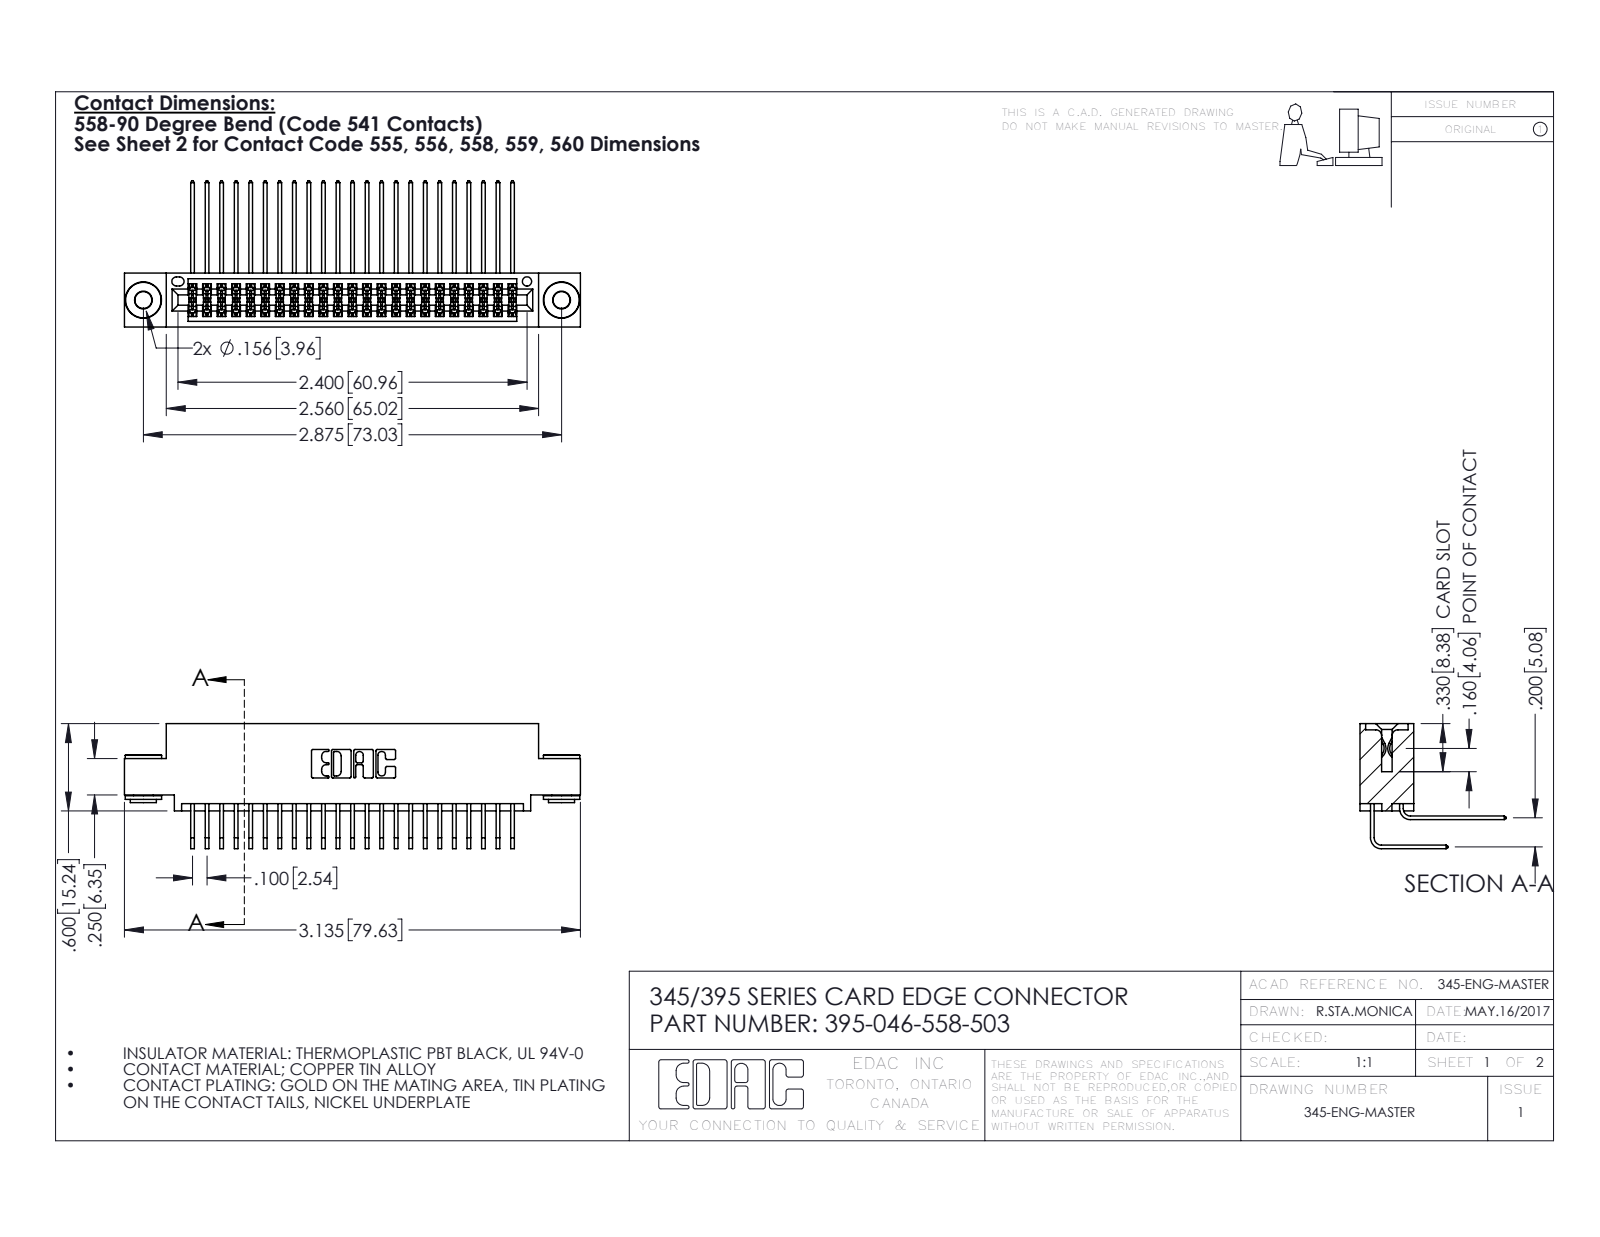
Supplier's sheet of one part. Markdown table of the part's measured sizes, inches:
| quantity | value |
| --- | --- |
| part name | 345-292-001_558 Tail - 2; 345 Part_0.110 Offset - 0.156 Dia-TH; 395-046-558-503; 345-292-001_558 559 Tail - 1 (+1 more) |
| STEP written by | SolidWorks 2016 (CONFIG_CONTROL_DESIGN) |
| units | inches |
| bodies | 49 solids, 2560 faces (1704 planar, 848 cylindrical, 8 other) |
| overall size | 3.135 × 1.005 × 0.859 |
| volume | 0.474 in³ |
| surface area | 19.63 in² |
| round holes (diameter × count) | 0.116 × 2, 0.156 × 2, 0.064 × 1 |
| round bosses / shafts (diameter × count) | 0.25 × 2, 0.18 × 2, 0.136 × 2 |
| partial cylindrical surfaces (radius × count) | 0.006 × 70, 0.01 × 22, 0.007 × 6, 0.031 × 6, 0.026 × 3, 0.014 × 2, 0.019 × 2, 0.022 × 2 |
| main face-to-face distances | 0.072, 0.298, 0.2, 0.37, 0.025, 0.098, 0.272, 0.225, 0.025, 0.175 |
| hole center spacings | 0.27, 2.641, 2.875 |
